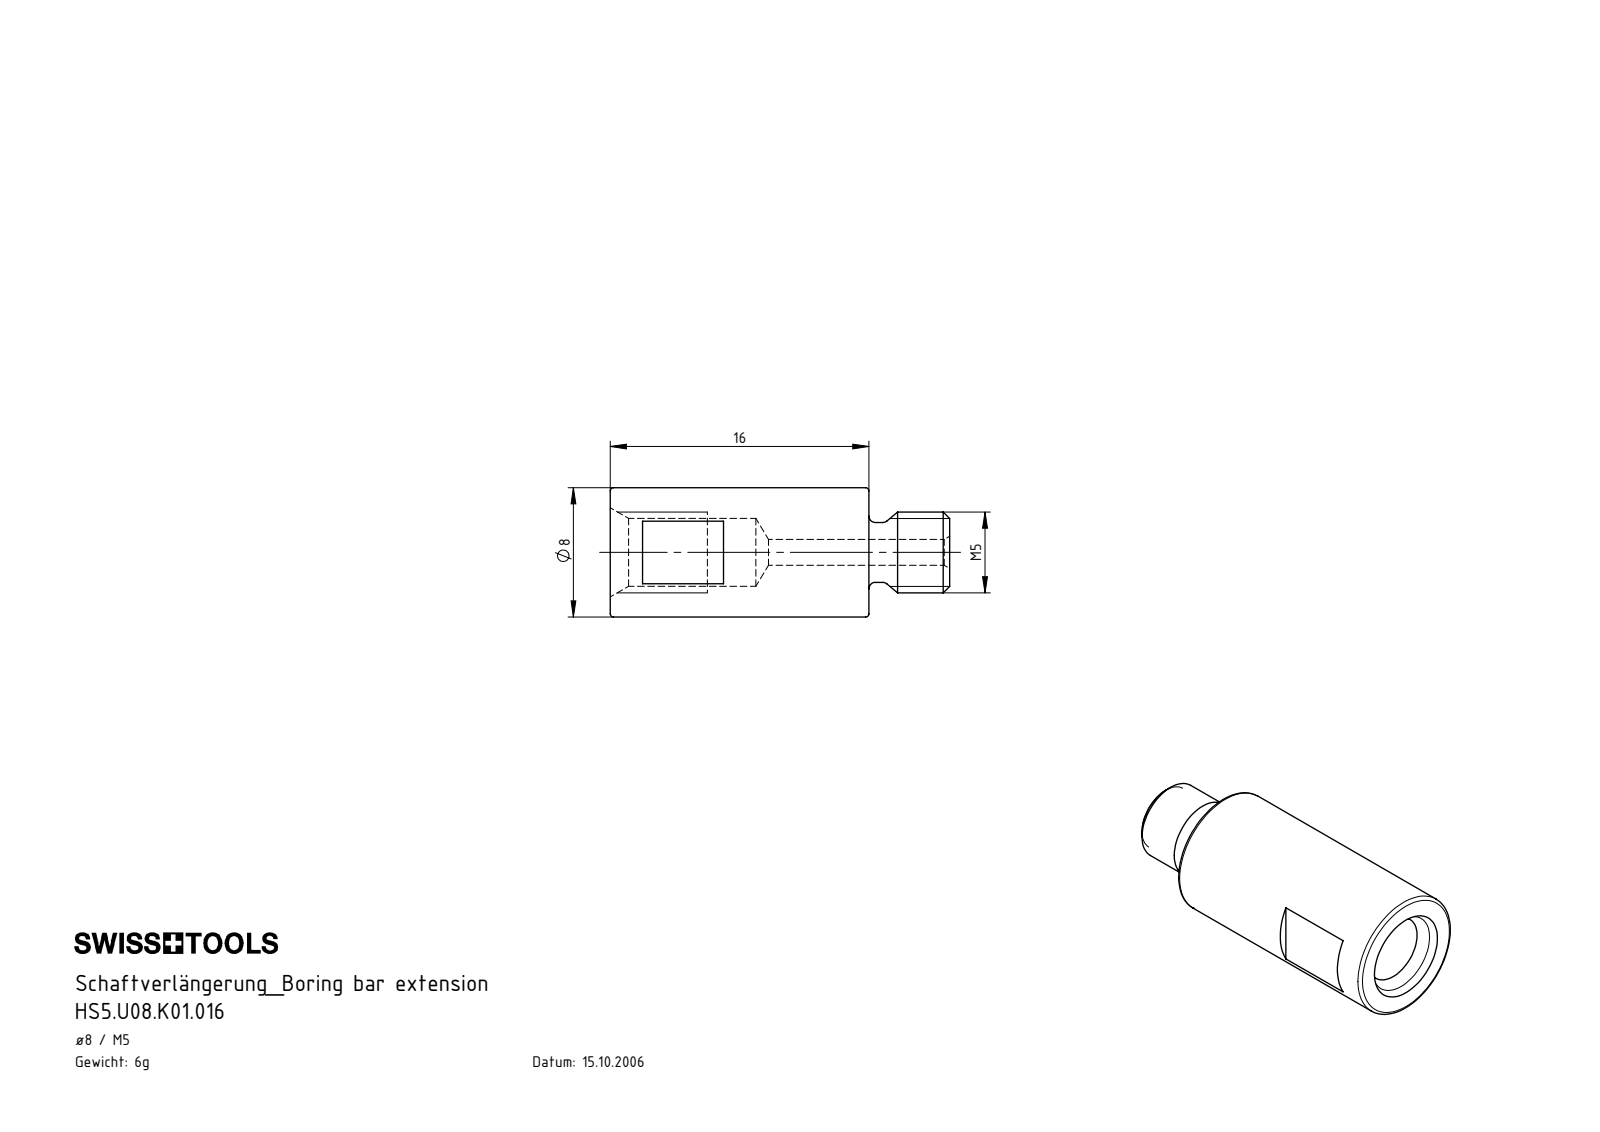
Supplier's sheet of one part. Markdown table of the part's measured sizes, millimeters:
| quantity | value |
| --- | --- |
| part name | 5-U.8.K01.016_A |
| STEP written by | SolidWorks 2017 (AUTOMOTIVE_DESIGN) |
| units | millimeters |
| bodies | 1 solid, 37 faces (9 planar, 10 cylindrical, 18 other) |
| overall size | 21 × 8 × 8 |
| volume | 717 mm³ |
| surface area | 748 mm² |
| round holes (diameter × count) | 1.6 × 1, 4.2 × 1 |
| round bosses / shafts (diameter × count) | 8 × 1, 5 × 1, 3.7 × 1 |
| main face-to-face distances | 7, 16, 5, 21, 14, 19, 2, 9 |
